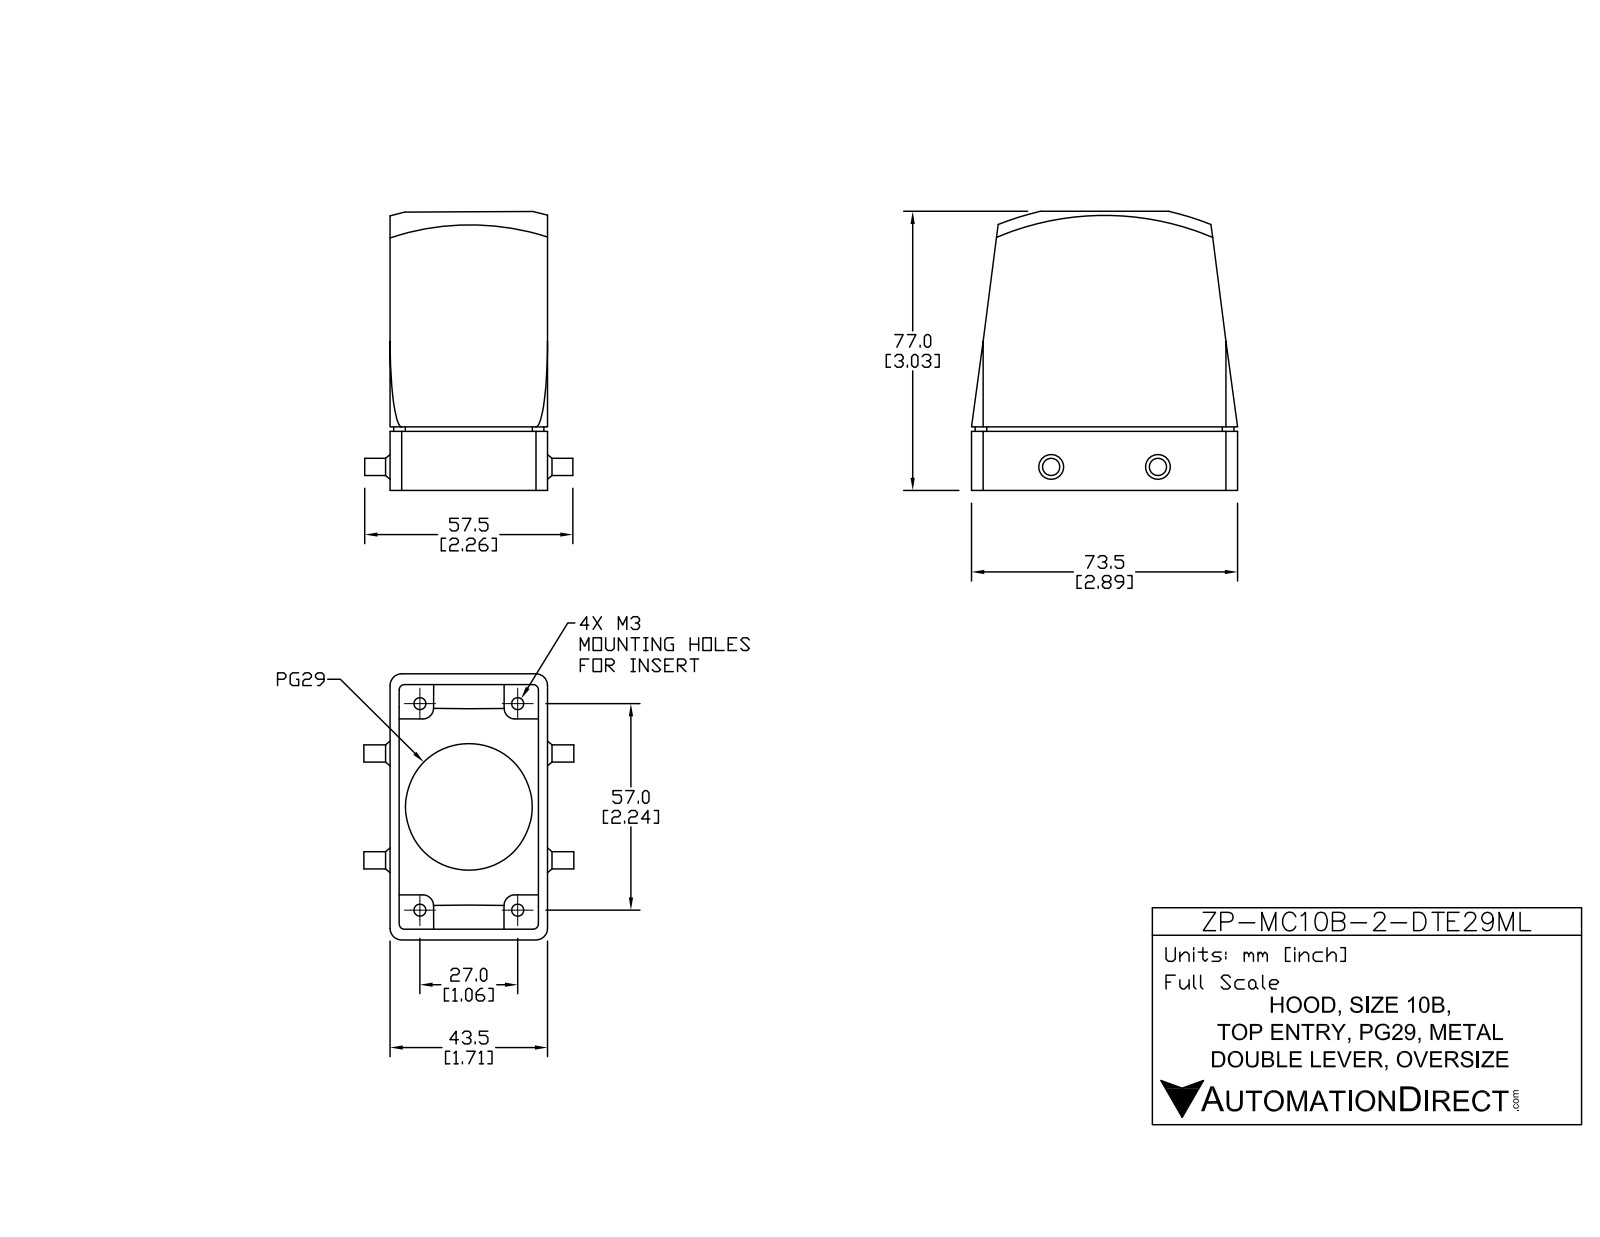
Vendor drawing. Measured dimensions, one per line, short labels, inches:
name: ZP-MC10B-2-DTE29ML
written by: SolidWorks 2011 (AUTOMOTIVE_DESIGN)
unit: in
bodies: 5 solids, 94 faces (54 planar, 30 cylindrical, 10 other)
size: 2.978 × 2.894 × 2.283
volume: 3.48 in³; area: 66.95 in²
holes: 4× ⌀0.138, 1× ⌀1.398
bosses: 2× ⌀0.187
rounds: 8× R0.126, 4× R0.028, 4× R0.118
face distances: 0.098, 1.614, 1.713, 1.516, 0.374, 2.287, 0.117, 0.491, 2.403, 2.777
hole spacings: 1.294, 1.14, 2.323, 2.587
